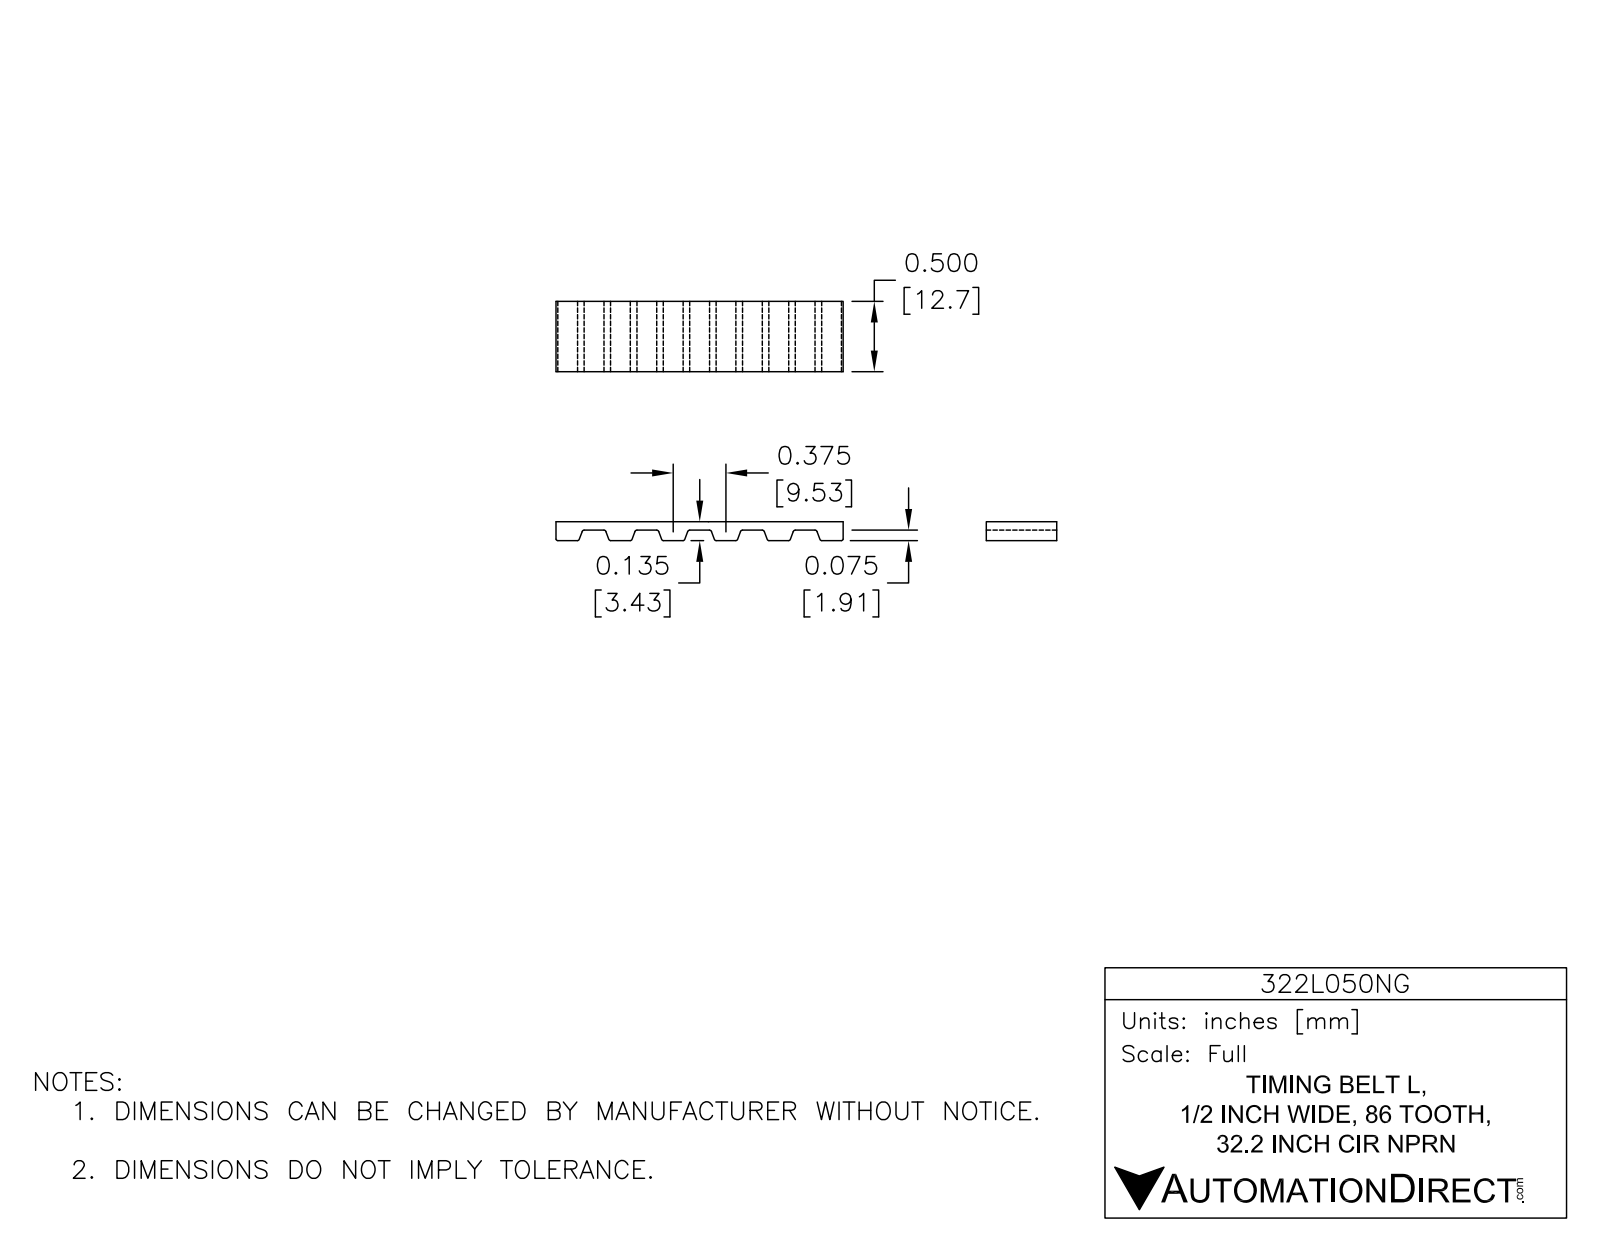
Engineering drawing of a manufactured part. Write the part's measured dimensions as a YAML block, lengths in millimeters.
part_name: "322L050NG"
step_written_by: "SolidWorks 2014 (AUTOMOTIVE_DESIGN)"
units: millimeters
bodies: {solids: 1, faces: 700, planar: 320, cylindrical: 380, other: 0}
overall_size: [366.1, 76.2, 12.7]
volume: 23910
surface_area: 26920
partial_cylinders:
  - {radius: 0.5, count: 340}
  - {radius: 36.4, count: 2}
  - {radius: 38.1, count: 2}
face_to_face_distances: [1.7, 74.5, 76.2, 12.7, 72.9, 3.6, 72.6, 1.9, 71, 69.1]
